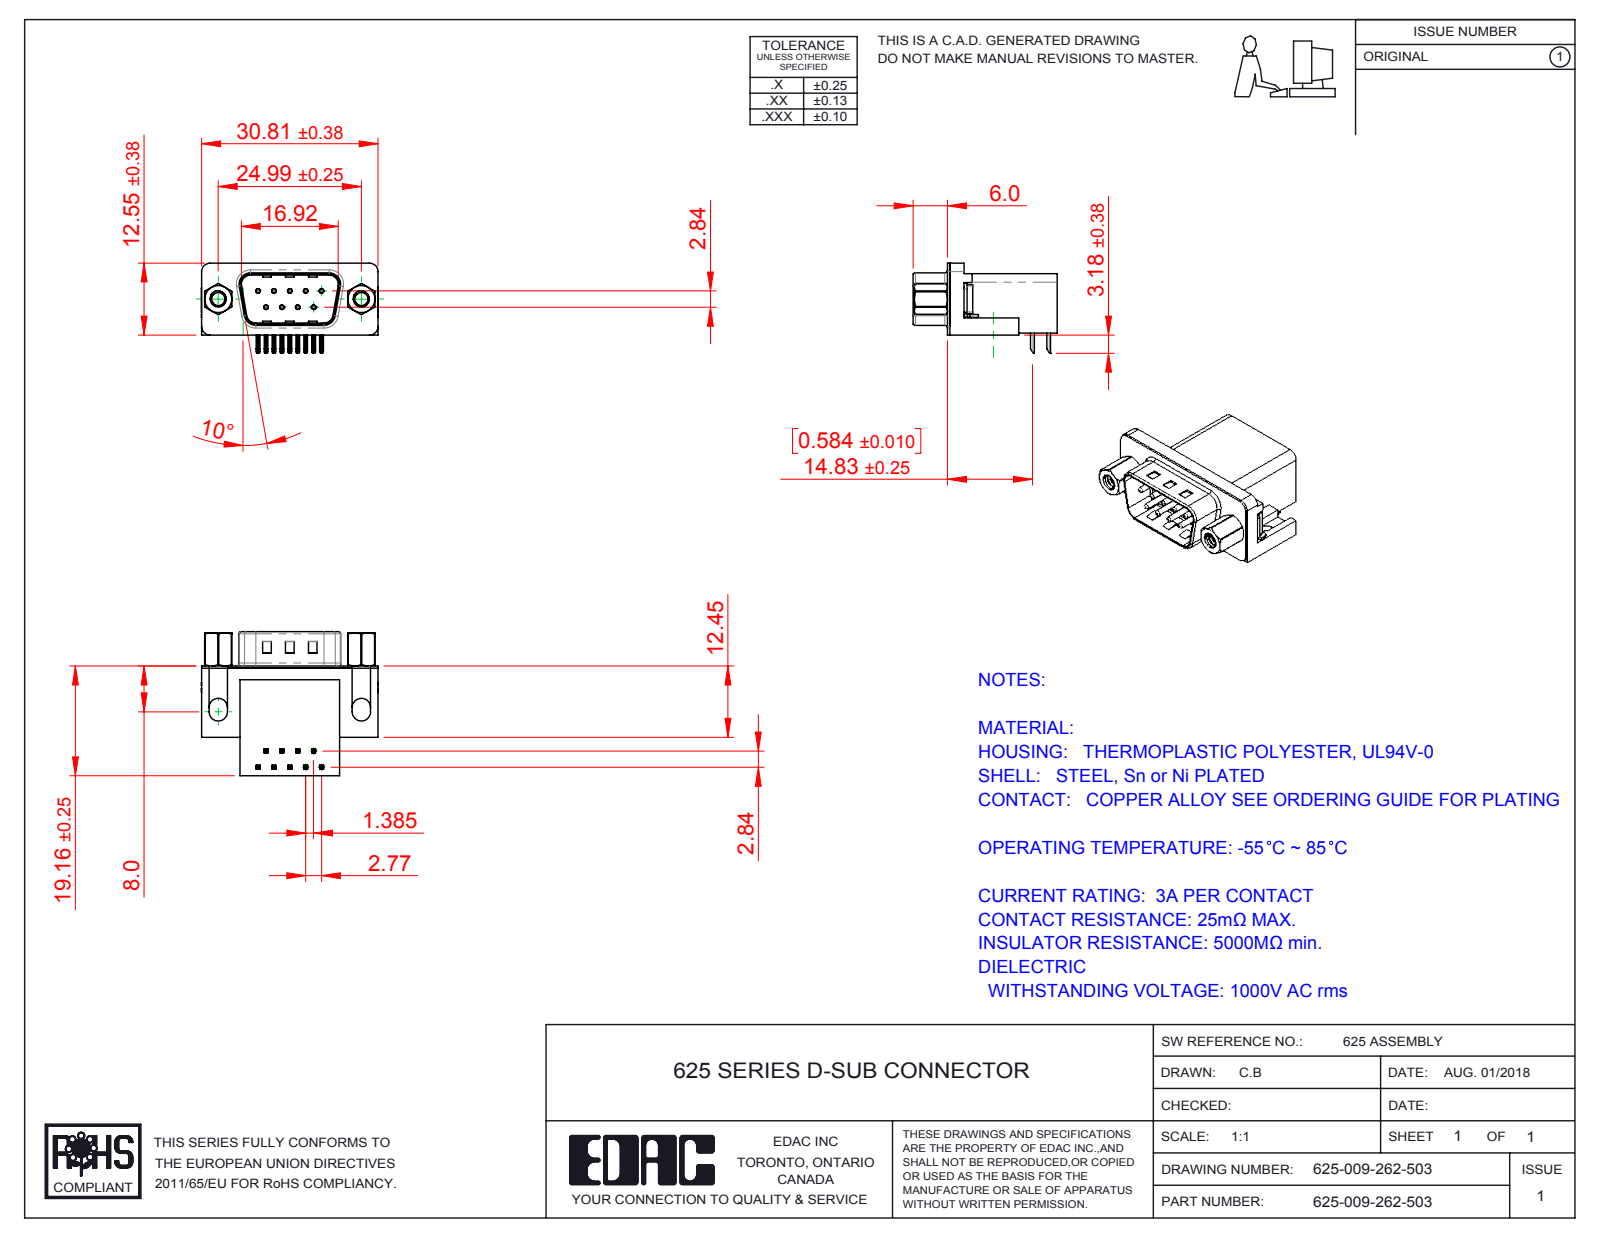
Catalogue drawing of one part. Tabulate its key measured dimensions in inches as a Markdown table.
| quantity | value |
| --- | --- |
| part name | 625 Contact Top; 625 Contact Bottom; 625 4-40 Threaded Rivet; 625 Non Board Mount (+4 more) |
| STEP written by | SolidWorks 2016 (CONFIG_CONTROL_DESIGN) |
| units | inches |
| bodies | 17 solids, 1117 faces (597 planar, 385 cylindrical, 135 other) |
| overall size | 1.216 × 0.991 × 0.619 |
| volume | 0.284 in³ |
| surface area | 8.215 in² |
| round holes (diameter × count) | 0.014 × 9, 0.031 × 9, 0.089 × 2, 0.09 × 2, 0.157 × 2, 0.189 × 2, 0.197 × 2 |
| round bosses / shafts (diameter × count) | 0.03 × 9, 0.193 × 2, 0.187 × 2, 0.154 × 2, 0.11 × 2 |
| partial cylindrical surfaces (radius × count) | 0.01 × 44, 0.005 × 18, 0.039 × 16, 0.02 × 9, 0.059 × 8, 0.063 × 8, 0.035 × 4, 0.079 × 4 |
| main face-to-face distances | 0.016, 0.407, 0.739, 0.754, 0.64, 0.098, 0.114, 0.014, 0.421, 0.264 |
| hole center spacings | 0.124, 0.109, 0.218, 0.198, 0.198, 0.327, 0.294, 0.295 |
